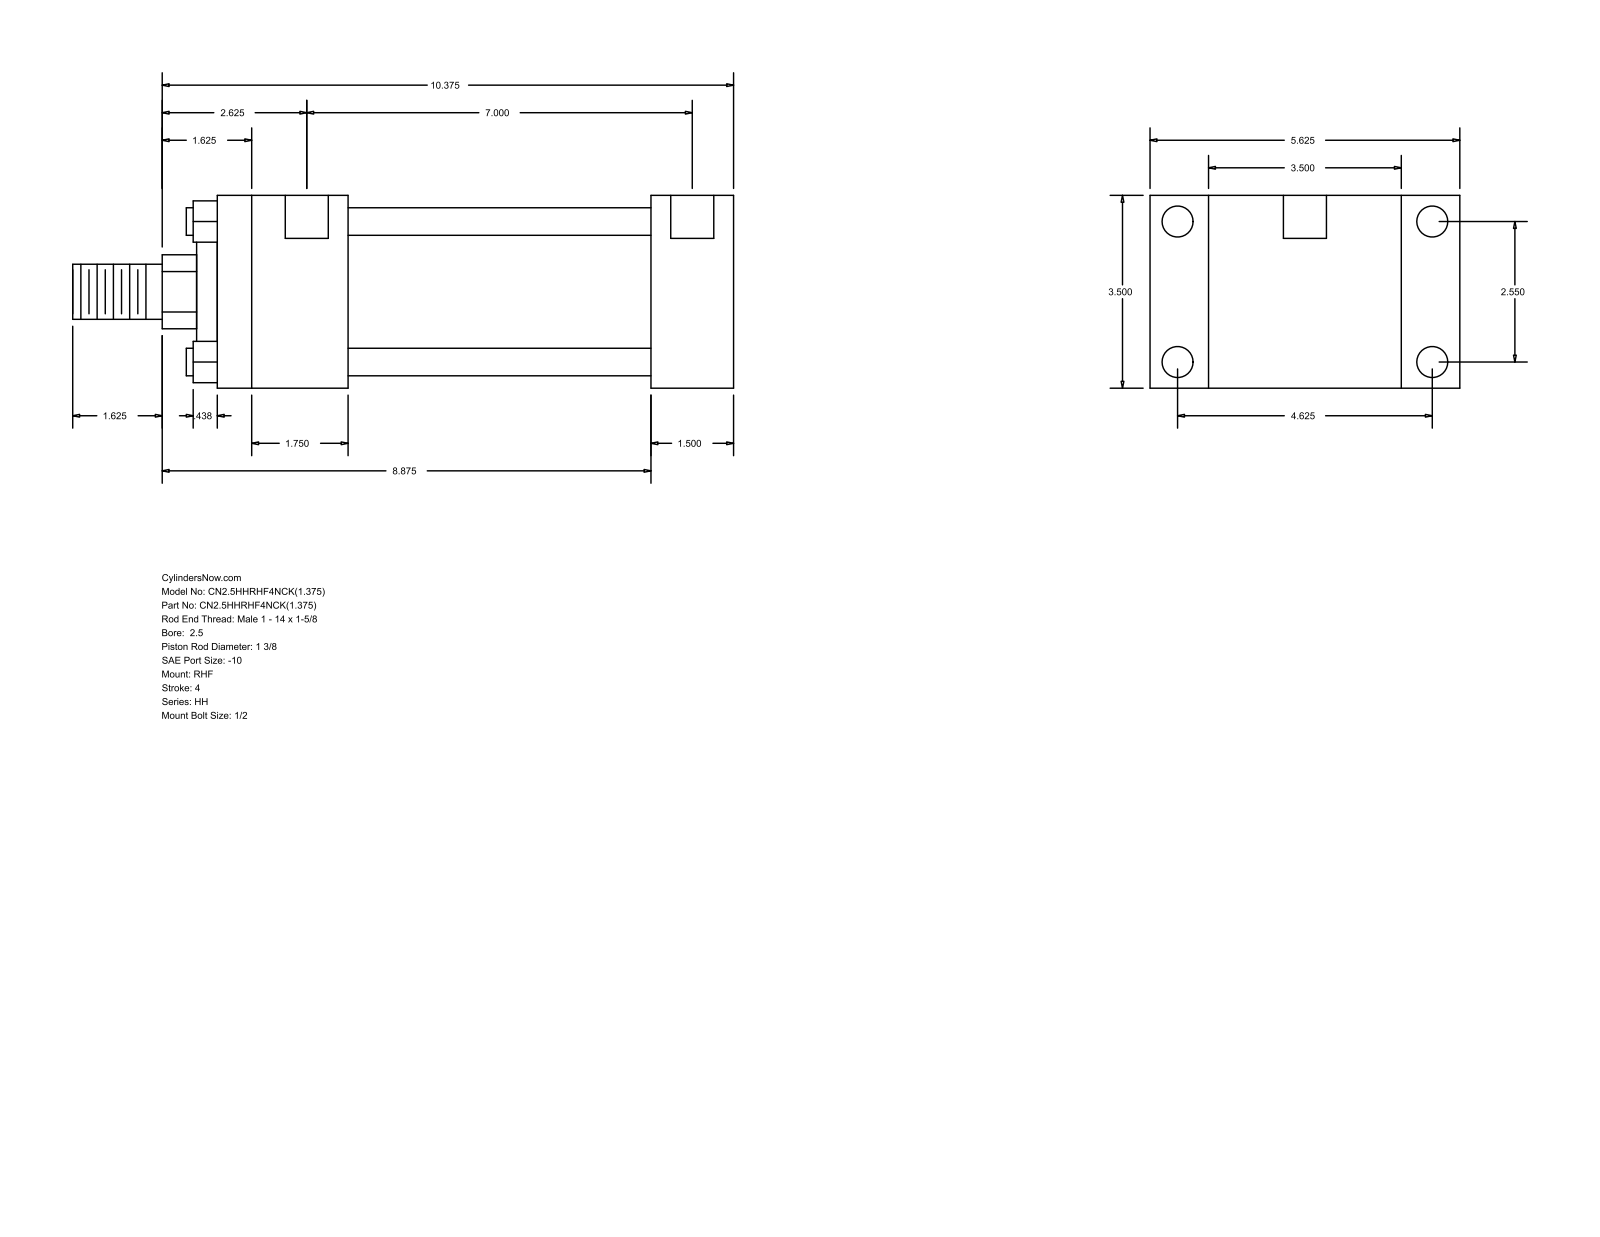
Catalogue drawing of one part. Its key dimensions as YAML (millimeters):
part_name: "HH_RHF__0250_1.375"
step_written_by: "GSSL Pune (CONFIG_CONTROL_DESIGN)"
units: millimeters
bodies: {solids: 0, faces: 88, planar: 60, cylindrical: 28, other: 0}
overall_size: [304.8, 142.88, 88.9]
round_holes:
  - {diameter: 5.56, count: 4}
  - {diameter: 14.3, count: 4}
  - {diameter: 19.84, count: 2}
round_bosses_or_shafts:
  - {diameter: 12.7, count: 4}
  - {diameter: 73.03, count: 1}
  - {diameter: 50.8, count: 1}
  - {diameter: 34.92, count: 1}
  - {diameter: 25.4, count: 1}
partial_cylinders:
  - {radius: 17.06, count: 1}
face_to_face_distances: [88.9, 38.09, 26.99, 115.89, 200.03, 238.12, 142.88, 60.32, 139.71, 177.8]
hole_center_spacings: [64.76, 117.48, 134.15, 180.97, 1.58, 1.59, 177.8, 179.38]
